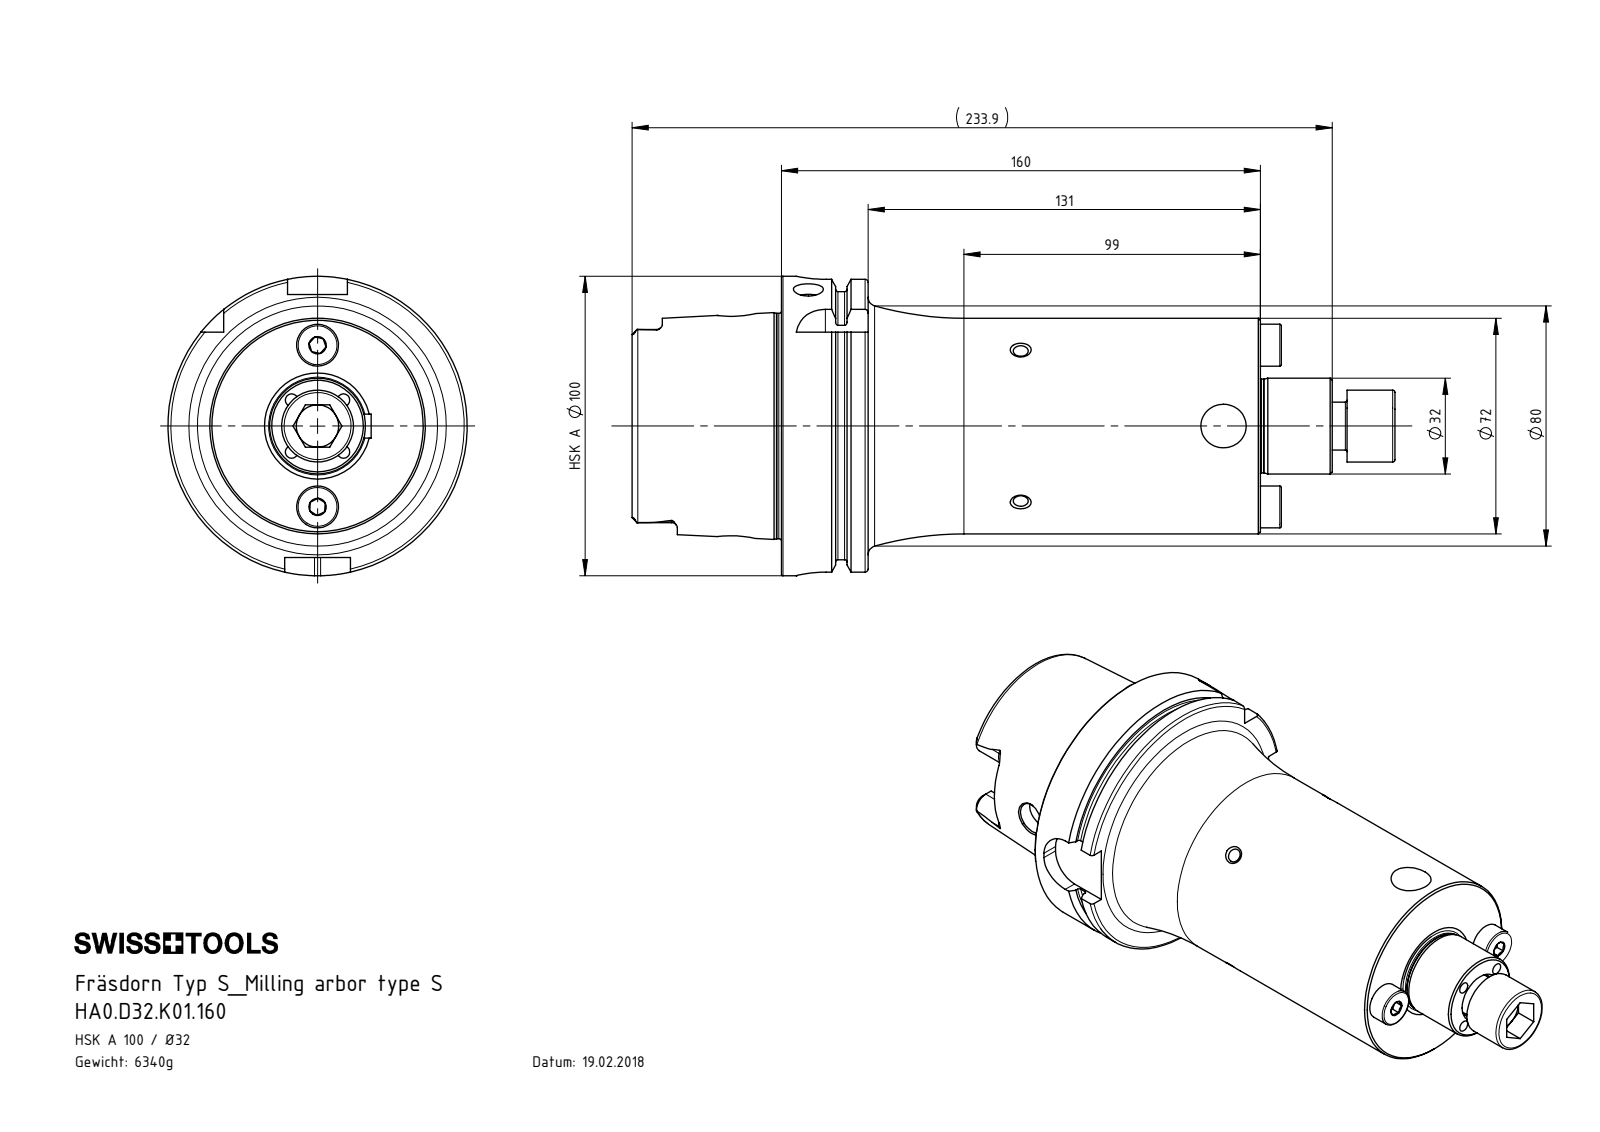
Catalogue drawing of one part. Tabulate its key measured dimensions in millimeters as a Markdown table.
| quantity | value |
| --- | --- |
| part name | DIN 6885 - 8x7x16; D32-ER2.001.022_B; HA0-D32.K01.160_D_Fertigbearbeitung; D32-ER1.002.035_A (+1 more) |
| STEP written by | SolidWorks 2017 (AUTOMOTIVE_DESIGN) |
| units | millimeters |
| bodies | 5 solids, 371 faces (89 planar, 119 cylindrical, 163 other) |
| overall size | 254.9 × 100 × 100 |
| volume | 807 687 mm³ |
| surface area | 98 032 mm² |
| round holes (diameter × count) | 4.2 × 6, 5 × 6, 12 × 4, 10 × 3, 14 × 1, 17 × 1, 22.5 × 1, 26 × 1, 53 × 1, 63 × 1 |
| round bosses / shafts (diameter × count) | 14 × 2, 6 × 2, 4.6 × 2, 100 × 1, 91.95 × 1, 75.26 × 1, 72 × 1, 32 × 1 |
| partial cylindrical surfaces (radius × count) | 1.9 × 6, 4 × 4, 4.88 × 4, 10 × 4 |
| main face-to-face distances | 160, 28.95, 131.05, 12.45, 16.5, 147.55, 49.9, 62.35, 78.85, 209.9 |
| hole center spacings | 12.25, 17.32, 20.28, 36.7, 70.05, 24.49, 27, 54 |
